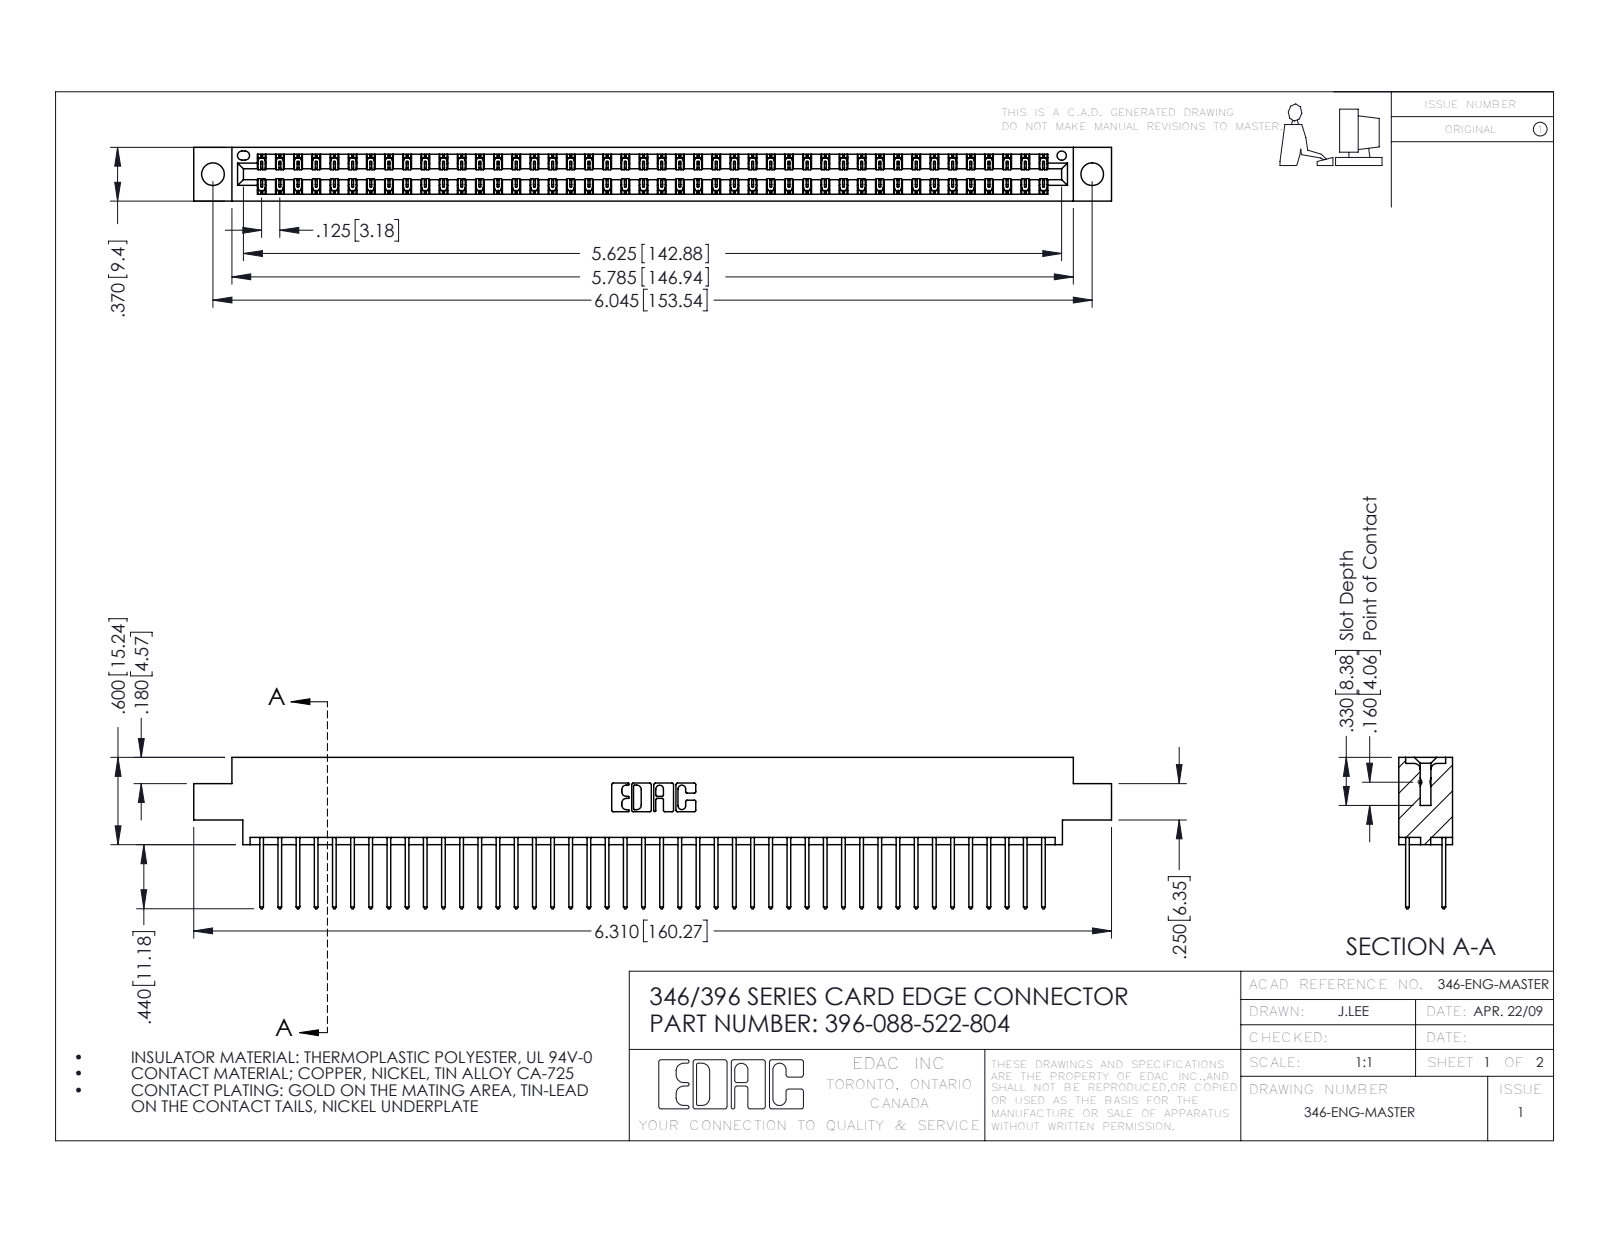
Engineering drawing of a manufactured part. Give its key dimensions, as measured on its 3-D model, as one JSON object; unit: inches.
{"part_name": "346 Part_0.170 Offset - 0.156 Dia-TH; 345-292-001_345-293-122; 396-088-522-804", "step_written_by": "SolidWorks 2016 (CONFIG_CONTROL_DESIGN)", "units": "inches", "bodies": {"solids": 89, "faces": 4702, "planar": 3160, "cylindrical": 1542, "other": 0}, "overall_size": [6.31, 1.04, 0.37], "volume_in3": 0.954, "surface_area_in2": 34.95, "round_holes": [[0.156, 2], [0.064, 1]], "partial_cylinders_radius": [[0.006, 132], [0.01, 88], [0.01, 22], [0.007, 6], [0.031, 6], [0.026, 3], [0.014, 2], [0.022, 2]], "face_to_face_distances": [0.048, 0.322, 0.25, 0.37, 0.072, 0.298, 0.025, 0.275, 0.148, 0.222], "hole_center_spacings": [0.246, 5.836, 6.045]}
